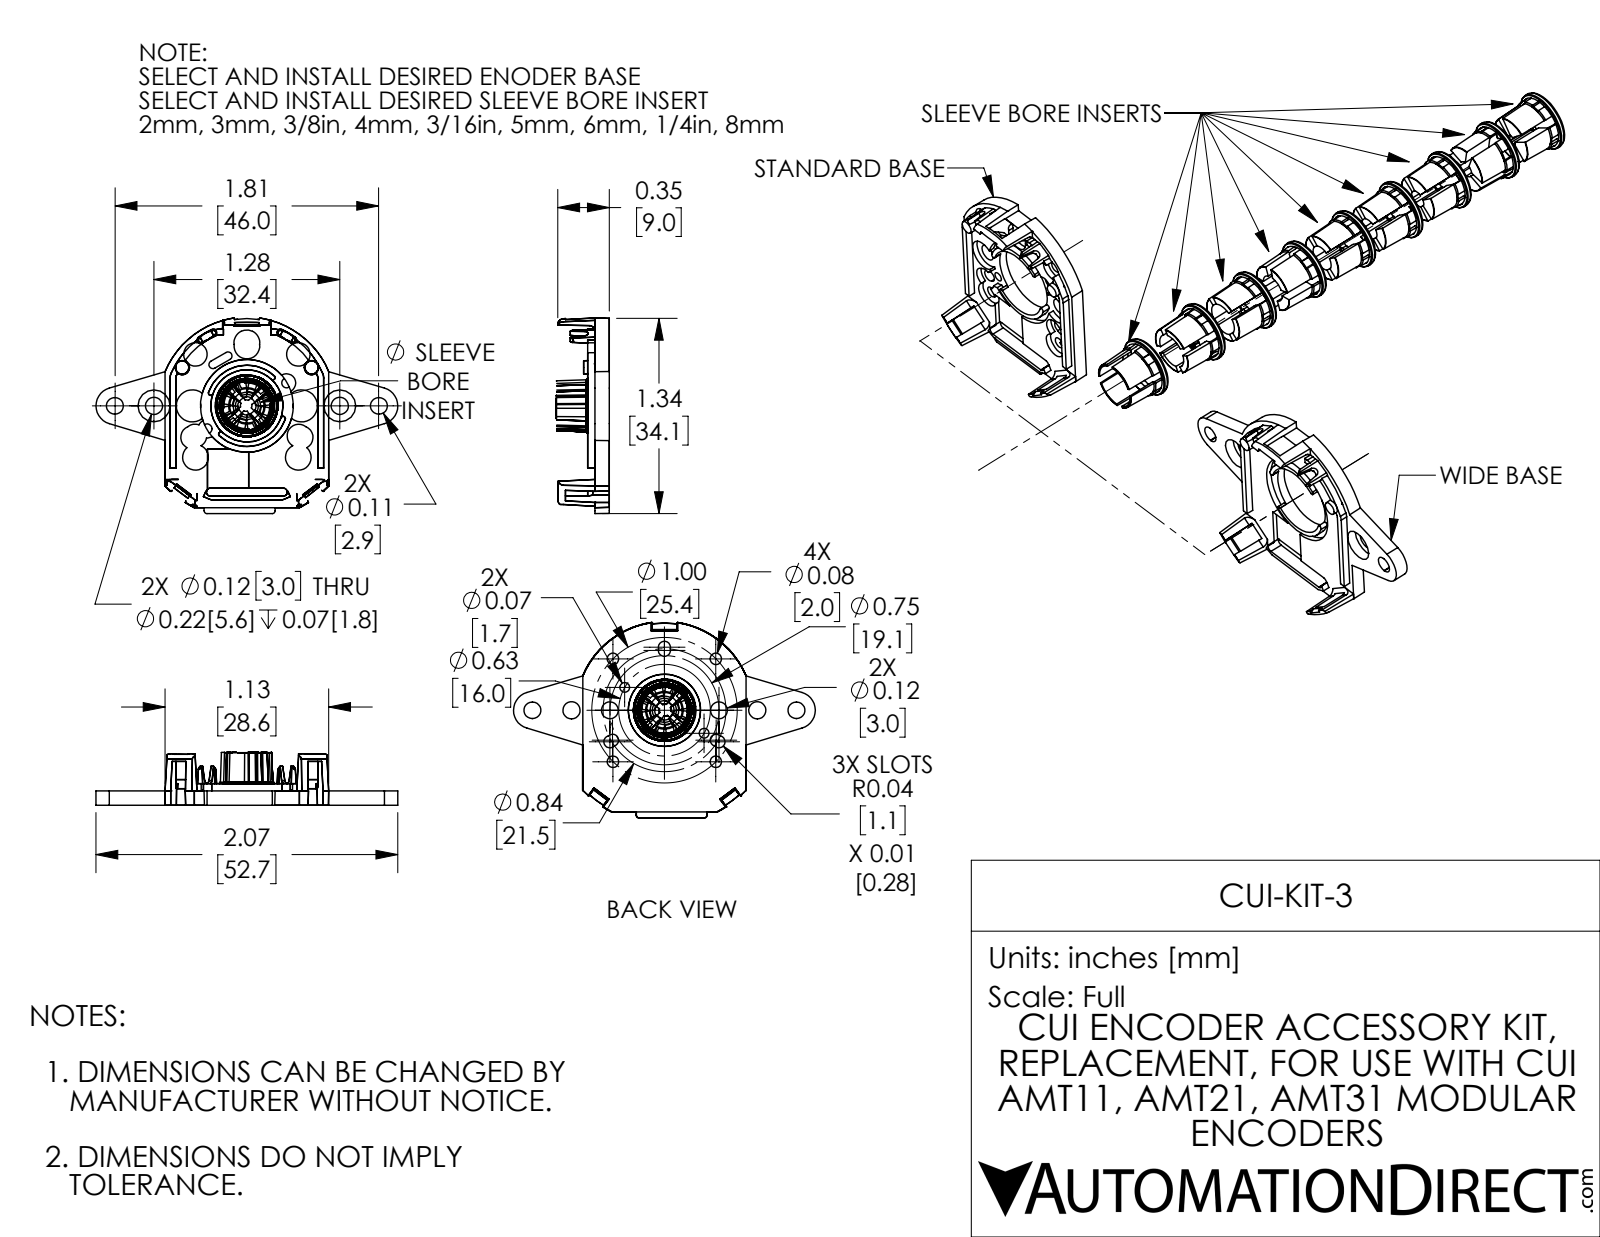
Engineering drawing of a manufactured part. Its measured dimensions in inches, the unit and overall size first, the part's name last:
Units: inches
Overall size (bounding box): 4.573 × 4.031 × 1.344
Round holes (diameter × count): ⌀0.079 ×4, ⌀0.067 ×2, ⌀0.116 ×2, ⌀0.118 ×2, ⌀0.161 ×2, ⌀0.177 ×2, ⌀0.22 ×2, ⌀0.496 ×2, ⌀0.638 ×1
Round bosses / shafts (diameter × count): ⌀0.413 ×2, ⌀0.356 ×1
Partial cylindrical surfaces — rounded edges, fillets, slot ends (radius × count): R0.039 ×15, R0.079 ×9, R0.016 ×8, R0.041 ×6, R0.028 ×4, R0.03 ×4, R0.056 ×4, R0.08 ×4
Main face-to-face distances: 0.057, 0.098, 0.156, 0.039, 0.041, 0.029, 0.059, 0.03, 0.097, 0.213
Hole centre spacings: 0.354, 0.5, 0.707, 0.188, 0.212, 0.315, 0.517, 0.639
Volume: 0.348 in³ · Surface area: 15.36 in²
Bodies: 11 solids, 1362 faces (444 planar, 347 cylindrical, 571 other)
Part name (STEP PRODUCT): CUI-KIT-3
STEP written by: SolidWorks 2021 (AUTOMOTIVE_DESIGN)
